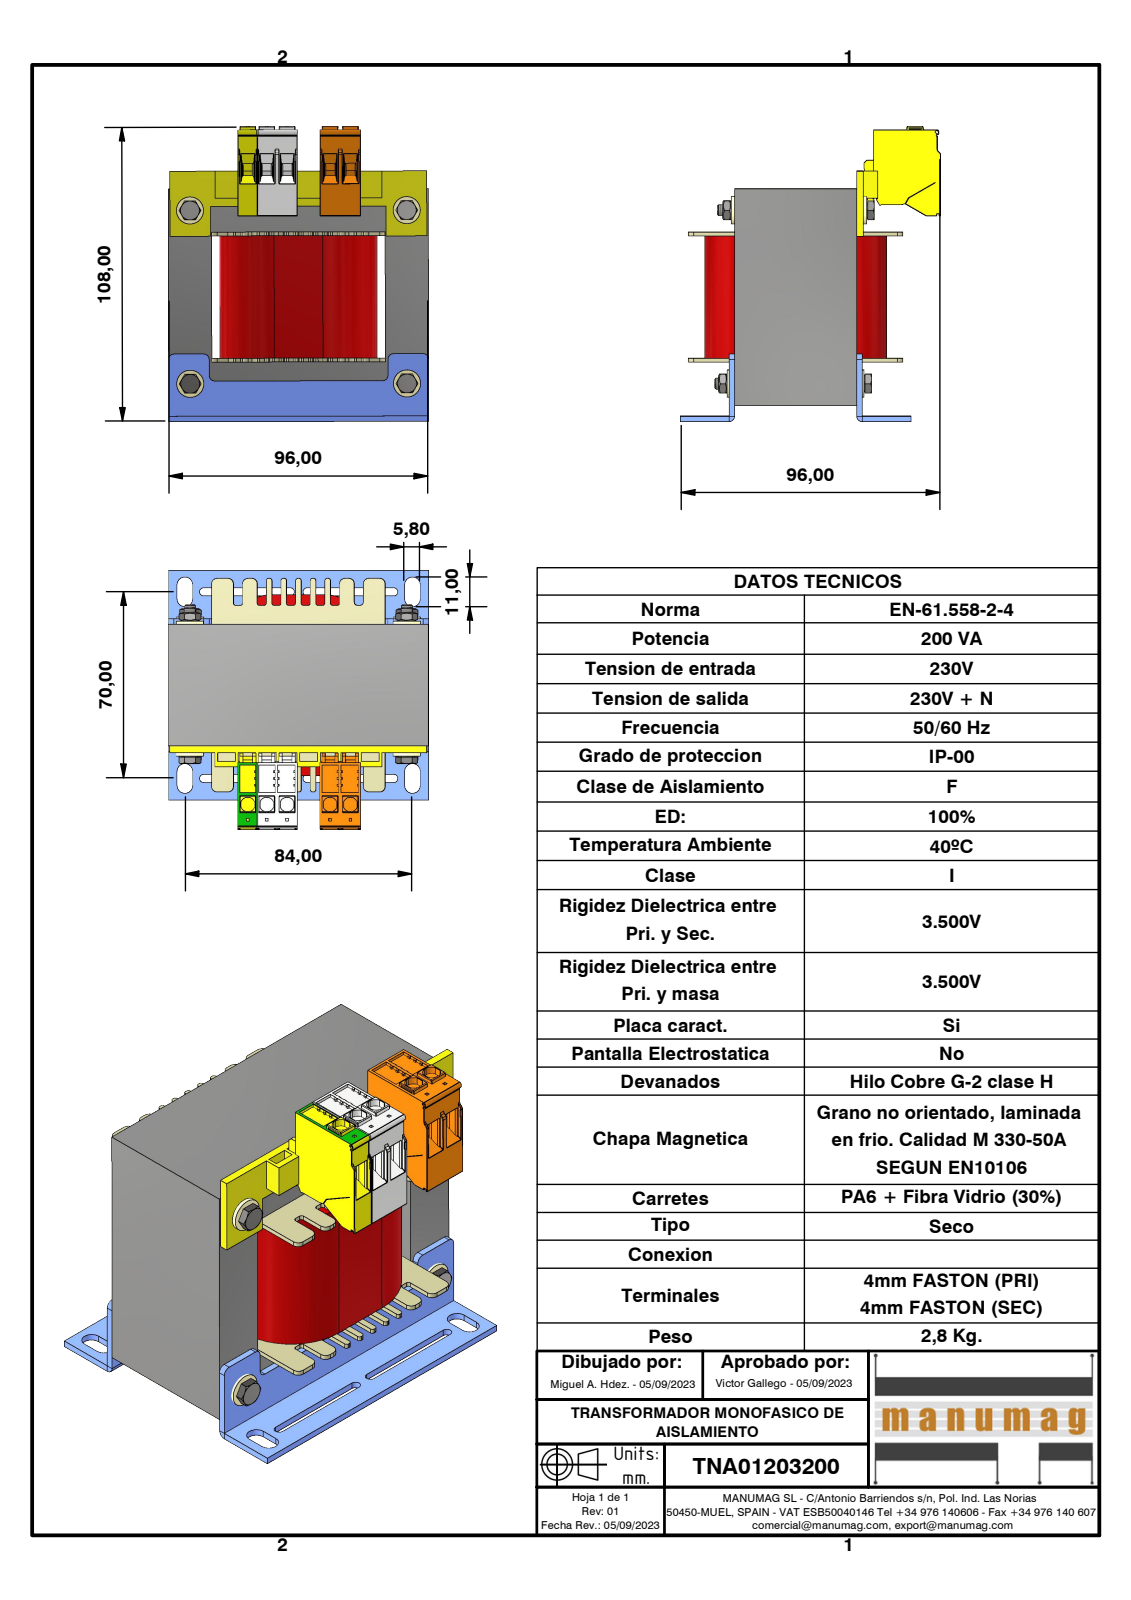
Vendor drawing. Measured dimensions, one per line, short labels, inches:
name: TNA01203200; EI96 x 80 - 45 (RC32); EI96; AF32DIN (+7 more)
written by: Autodesk Inventor 2023 (AUTOMOTIVE_DESIGN)
unit: in
bodies: 24 solids, 5325 faces (4333 planar, 688 cylindrical, 304 other)
size: 4.296 × 3.785 × 3.778
volume: 25.53 in³; area: 174.6 in²
holes: 4× ⌀0.128, 4× ⌀0.157, 4× ⌀0.217, 2× ⌀0.228
bosses: 4× ⌀0.394, 4× ⌀0.232, 4× ⌀0.193, 4× ⌀0.143
rounds: 216× R0.006, 102× R0.031, 74× R0.008, 38× R0.079, 19× R0.02, 12× R0.012, 10× R0.039, 8× R0.059
face distances: 1.772, 1.89, 0.079, 2.52, 0.631, 1.26, 0.63, 0.629, 3.151, 2.52
hole spacings: 2.52, 3.15, 4.033
